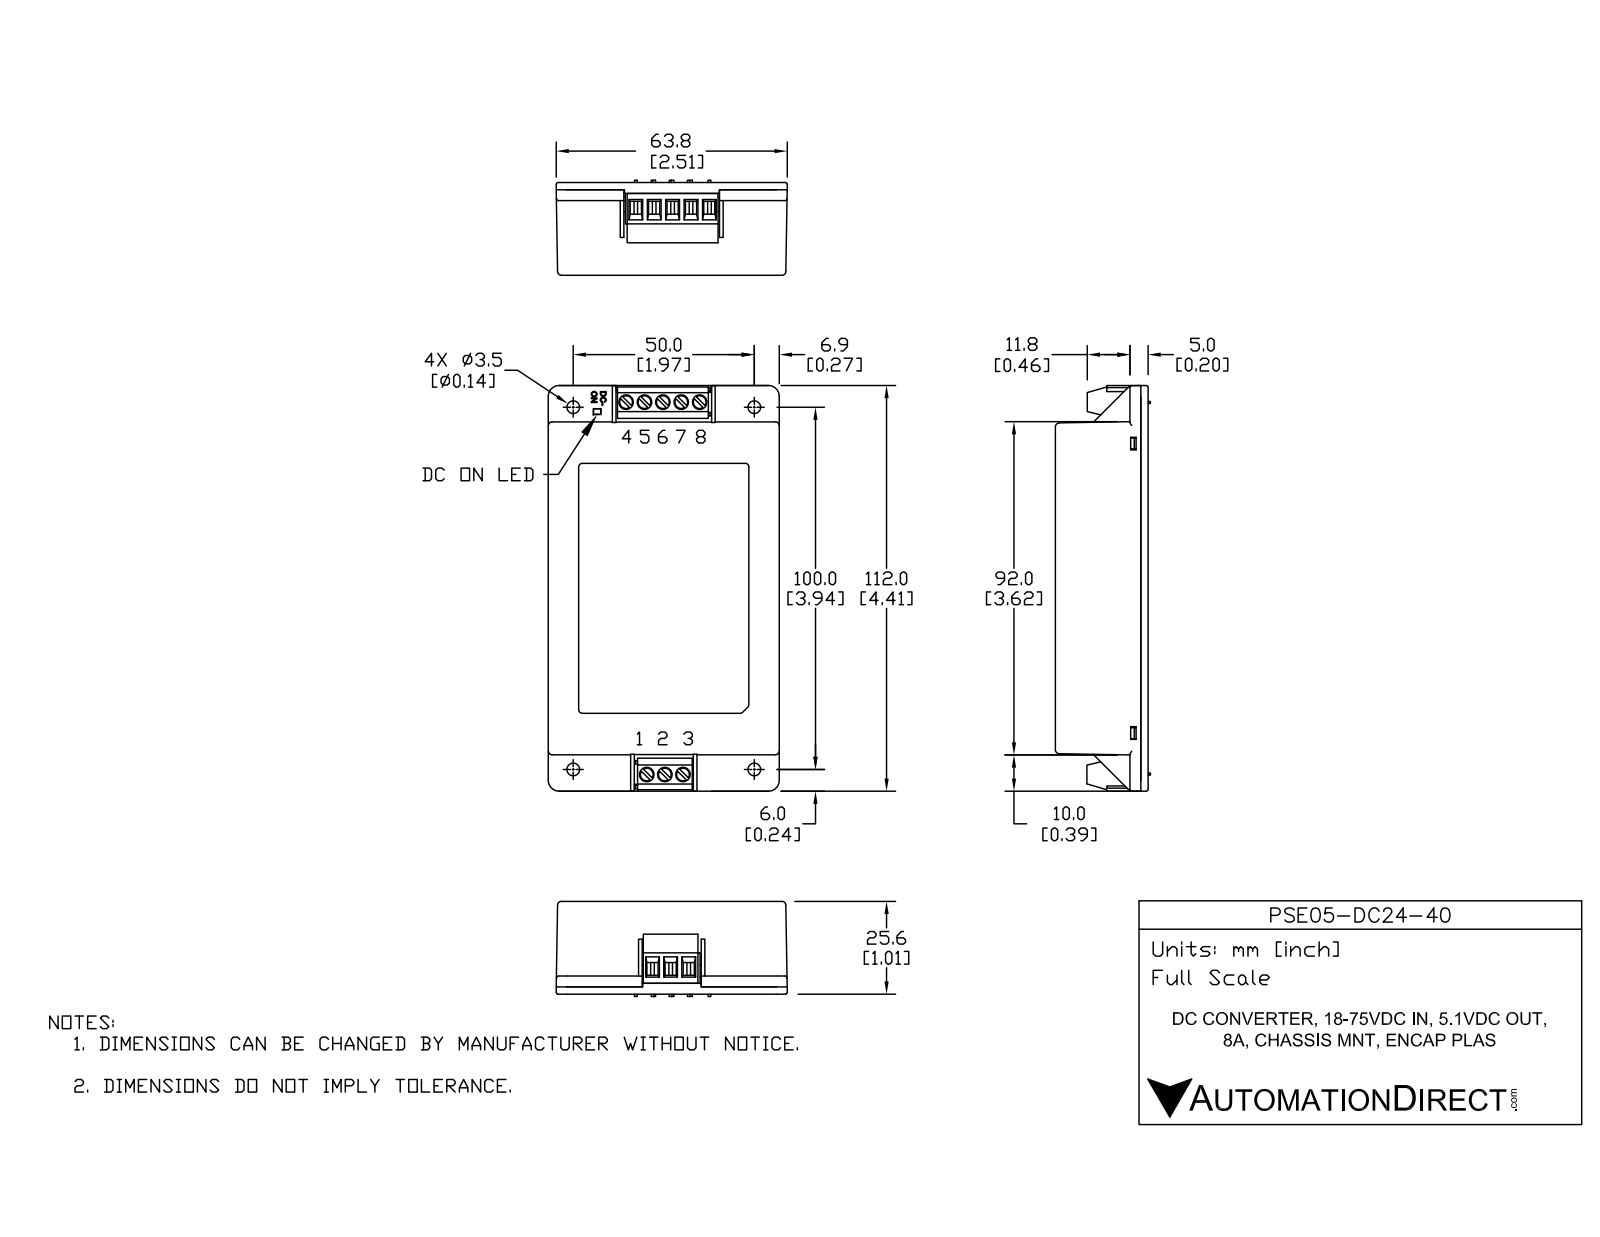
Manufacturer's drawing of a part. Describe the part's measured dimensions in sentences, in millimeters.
The part is named "PSE05-DC24-40". Its 3-D file was written by "SolidWorks 2019 (AUTOMOTIVE_DESIGN)". It is 12 solids with 282 faces: 222 planar, 54 cylindrical and 6 other. Overall it measures 112 by 63.8 by 25.6 millimeters. Its volume is 158 166 cubic millimeters and its surface area 40 616 square millimeters. Round holes: 8 of diameter 4, 4 of diameter 3.5. Round bosses or shafts: 8 of diameter 3.5. Partial cylindrical surfaces (rounded edges, fillets, slot ends): 4 of radius 3, 2 of radius 1.5. The main face-to-face distances are 2, 25.6, 23.6, 63.8, 3, 91.2, 1, 5, 20.6, 22.6. The hole center spacings are 5.08, 10.16, 102.8, 102.9, 5, 15.24, 50, 99.9.
